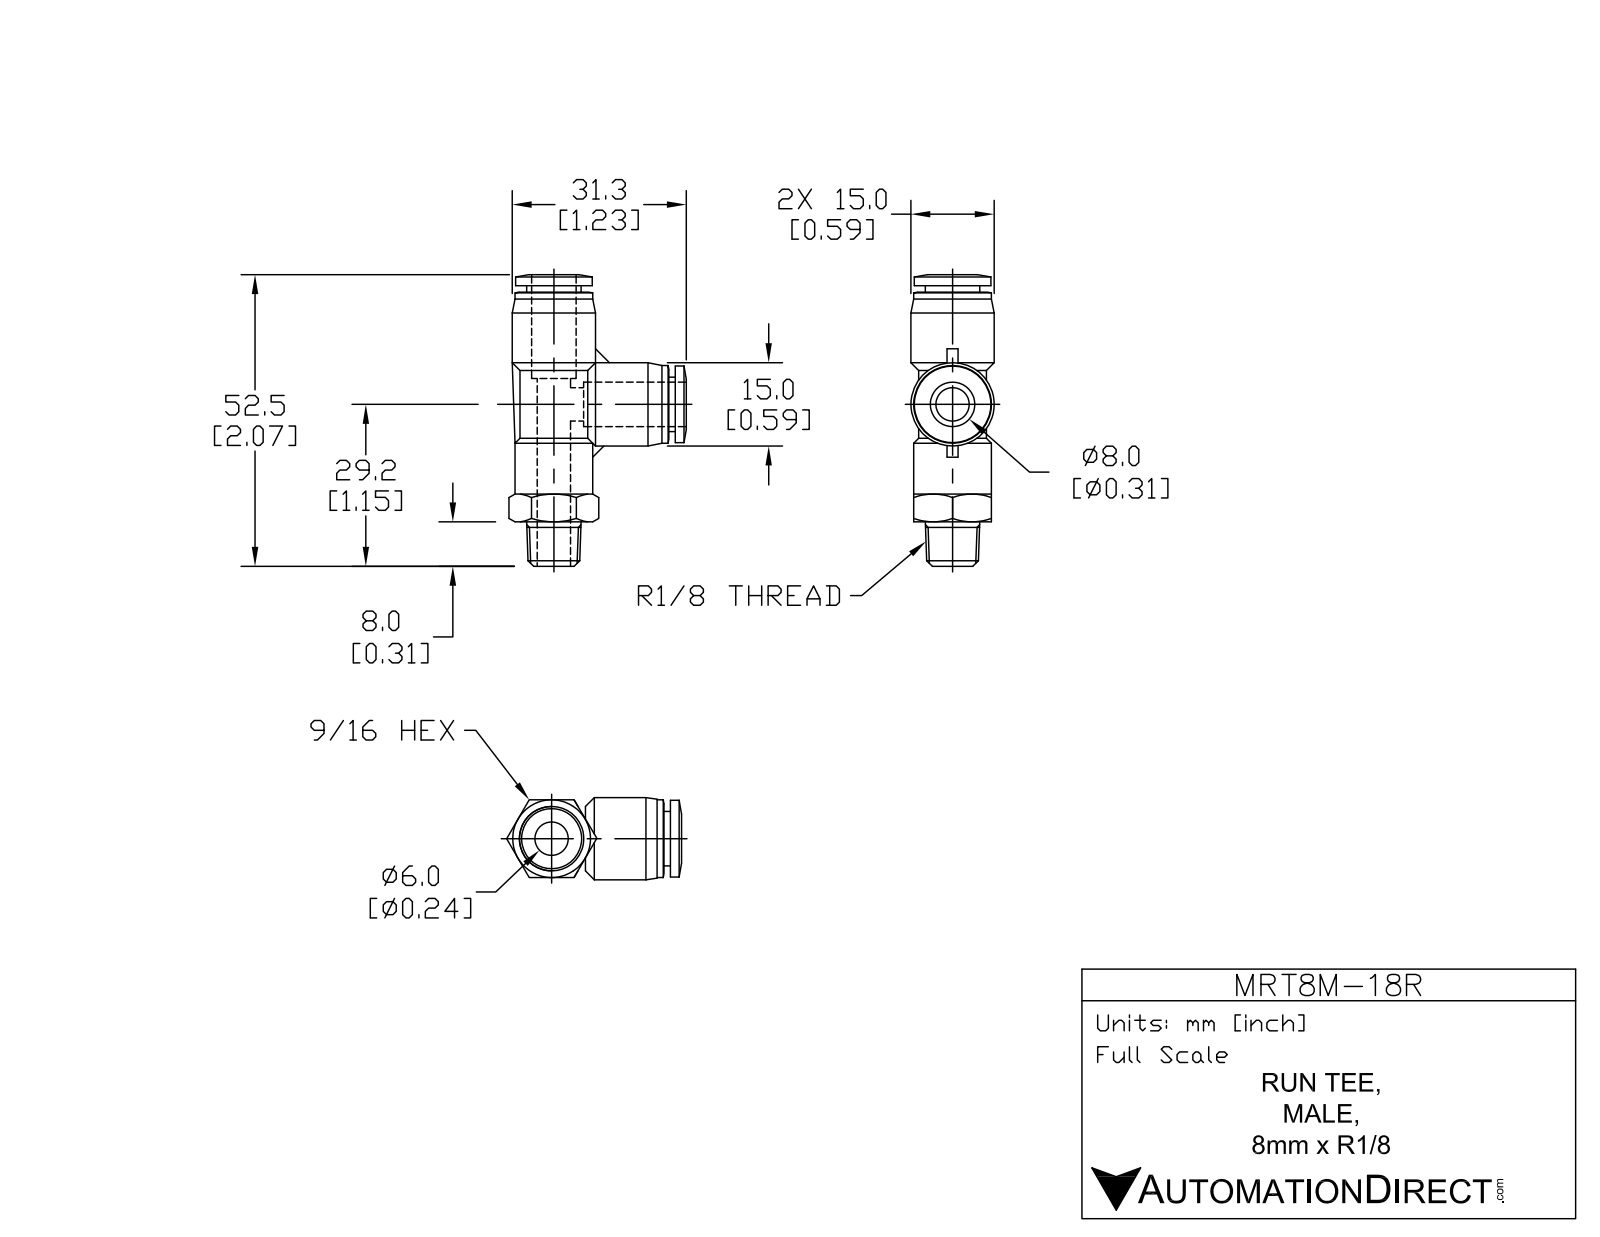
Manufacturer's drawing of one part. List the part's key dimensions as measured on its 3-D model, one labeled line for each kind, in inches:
Part name (STEP PRODUCT): MRT8M-18R
STEP written by: SolidWorks 2015 (AUTOMOTIVE_DESIGN)
Units: inches
Bodies: 1 solid, 99 faces (24 planar, 32 cylindrical, 43 other)
Overall size (bounding box): 2.051 × 1.238 × 0.591
Volume: 0.425 in³ · Surface area: 8.028 in²
Round holes (diameter × count): ⌀0.236 ×2, ⌀0.327 ×2
Round bosses / shafts (diameter × count): ⌀0.591 ×2, ⌀0.551 ×2, ⌀0.543 ×2, ⌀0.48 ×2, ⌀0.386 ×2
Main face-to-face distances: 0.551, 0.045, 1.657, 0.315, 0.596, 0.642, 1.612, 0.236, 0.079, 1.016
